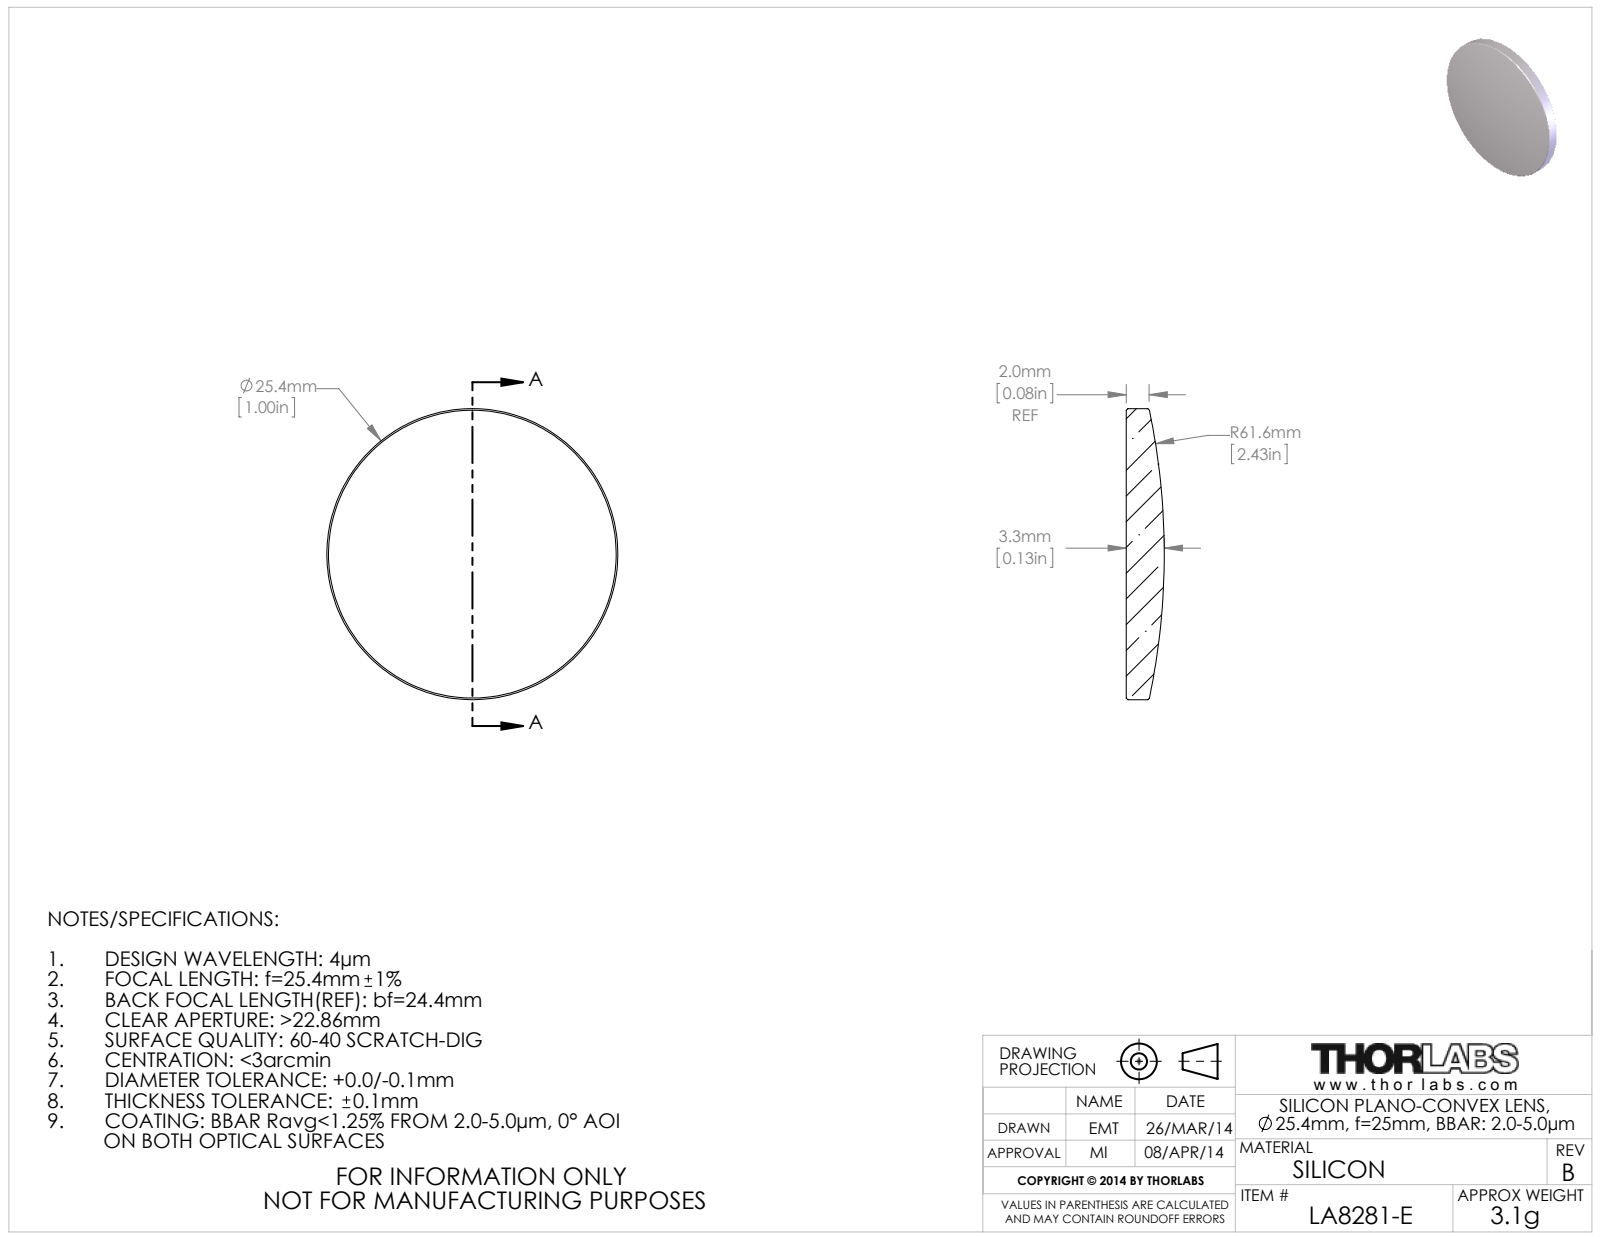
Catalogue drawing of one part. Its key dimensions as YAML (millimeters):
part_name: "20116-E0W"
step_written_by: "SolidWorks 2014 (CONFIG_CONTROL_DESIGN)"
units: millimeters
bodies: {solids: 1, faces: 9, planar: 1, cylindrical: 2, other: 6}
overall_size: [25.4, 25.4, 3.32]
volume: 1347
surface_area: 1167
round_bosses_or_shafts:
  - {diameter: 25.4, count: 1}
